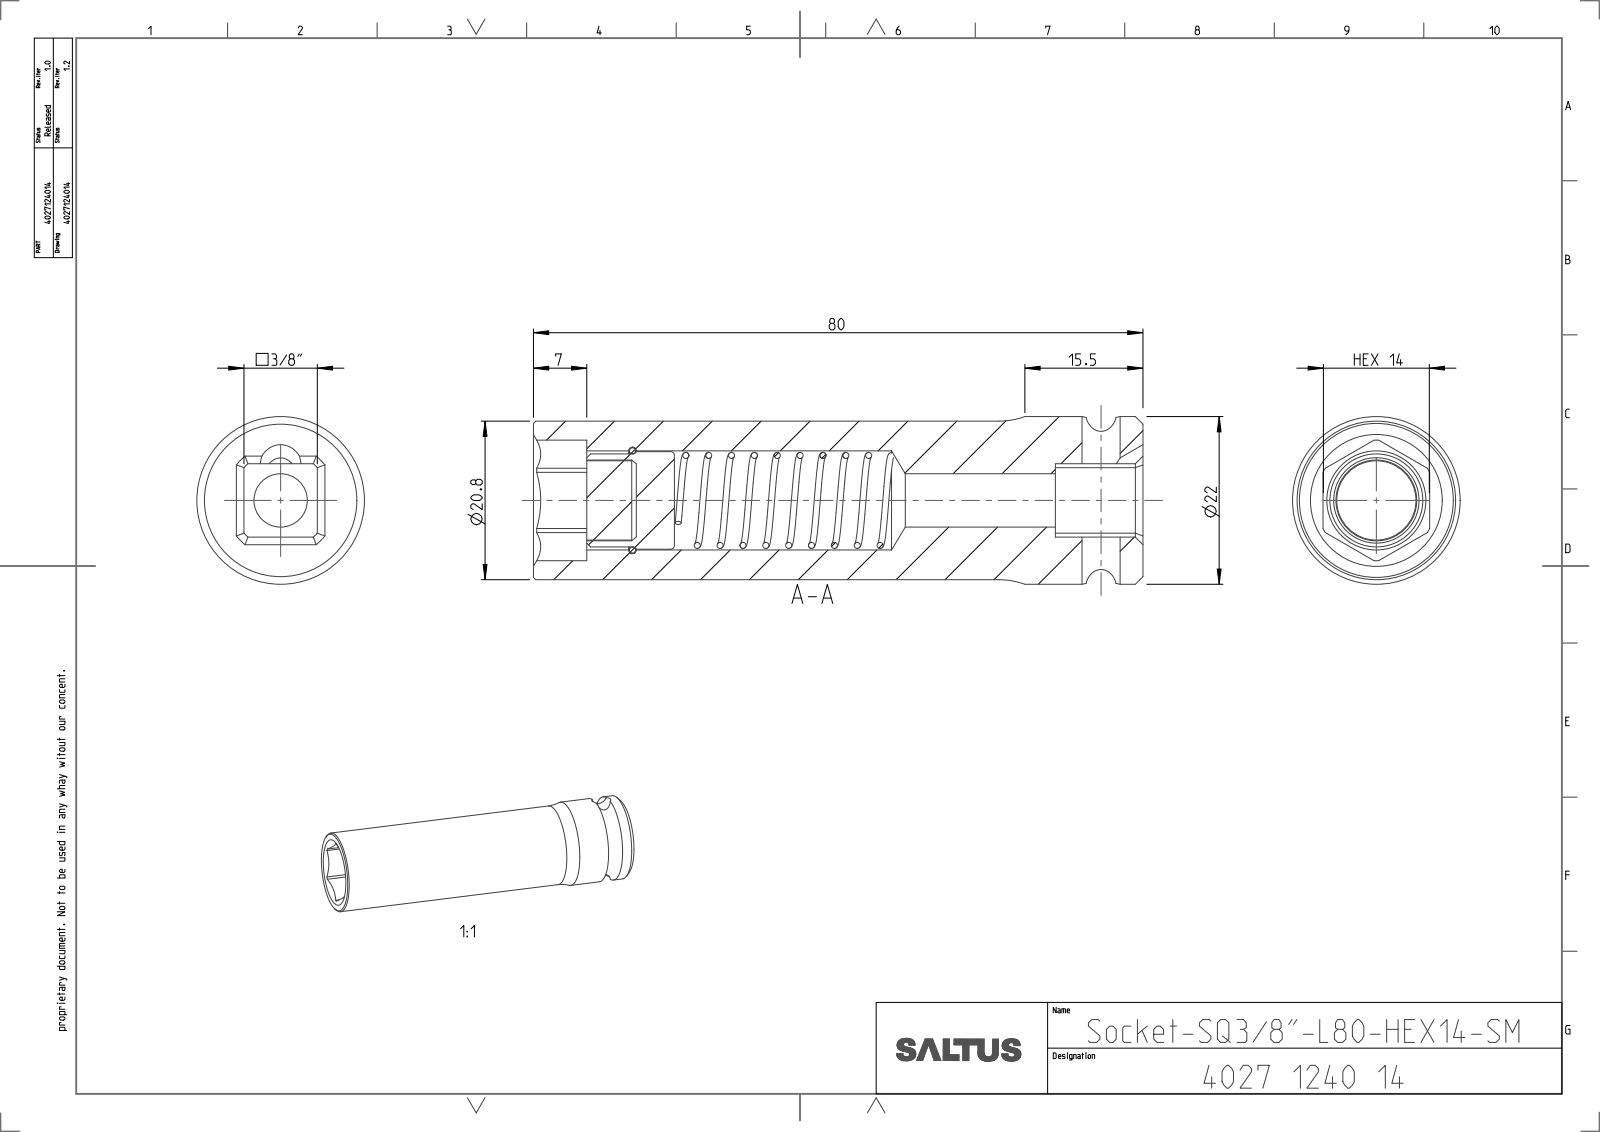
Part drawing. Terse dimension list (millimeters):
name: 4027124014
written by: CREO PARAMETRIC BY PTC INC, 2022414 (CONFIG_CONTROL_DESIGN)
unit: mm
bodies: 4 solids, 97 faces (26 planar, 35 cylindrical, 36 other)
size: 80 × 22 × 22
volume: 20 304 mm³; area: 11 079 mm²
holes: 1× ⌀5, 1× ⌀7, 1× ⌀10.6, 1× ⌀13
bosses: 1× ⌀22, 1× ⌀20.8, 1× ⌀12.8, 1× ⌀12.2, 1× ⌀10.4
rounds: 1× R3, 1× R6.45, 1× R7.91
face distances: 11.5, 61.5, 9.62, 14, 73, 2.19, 11.81, 7, 80, 18.5
